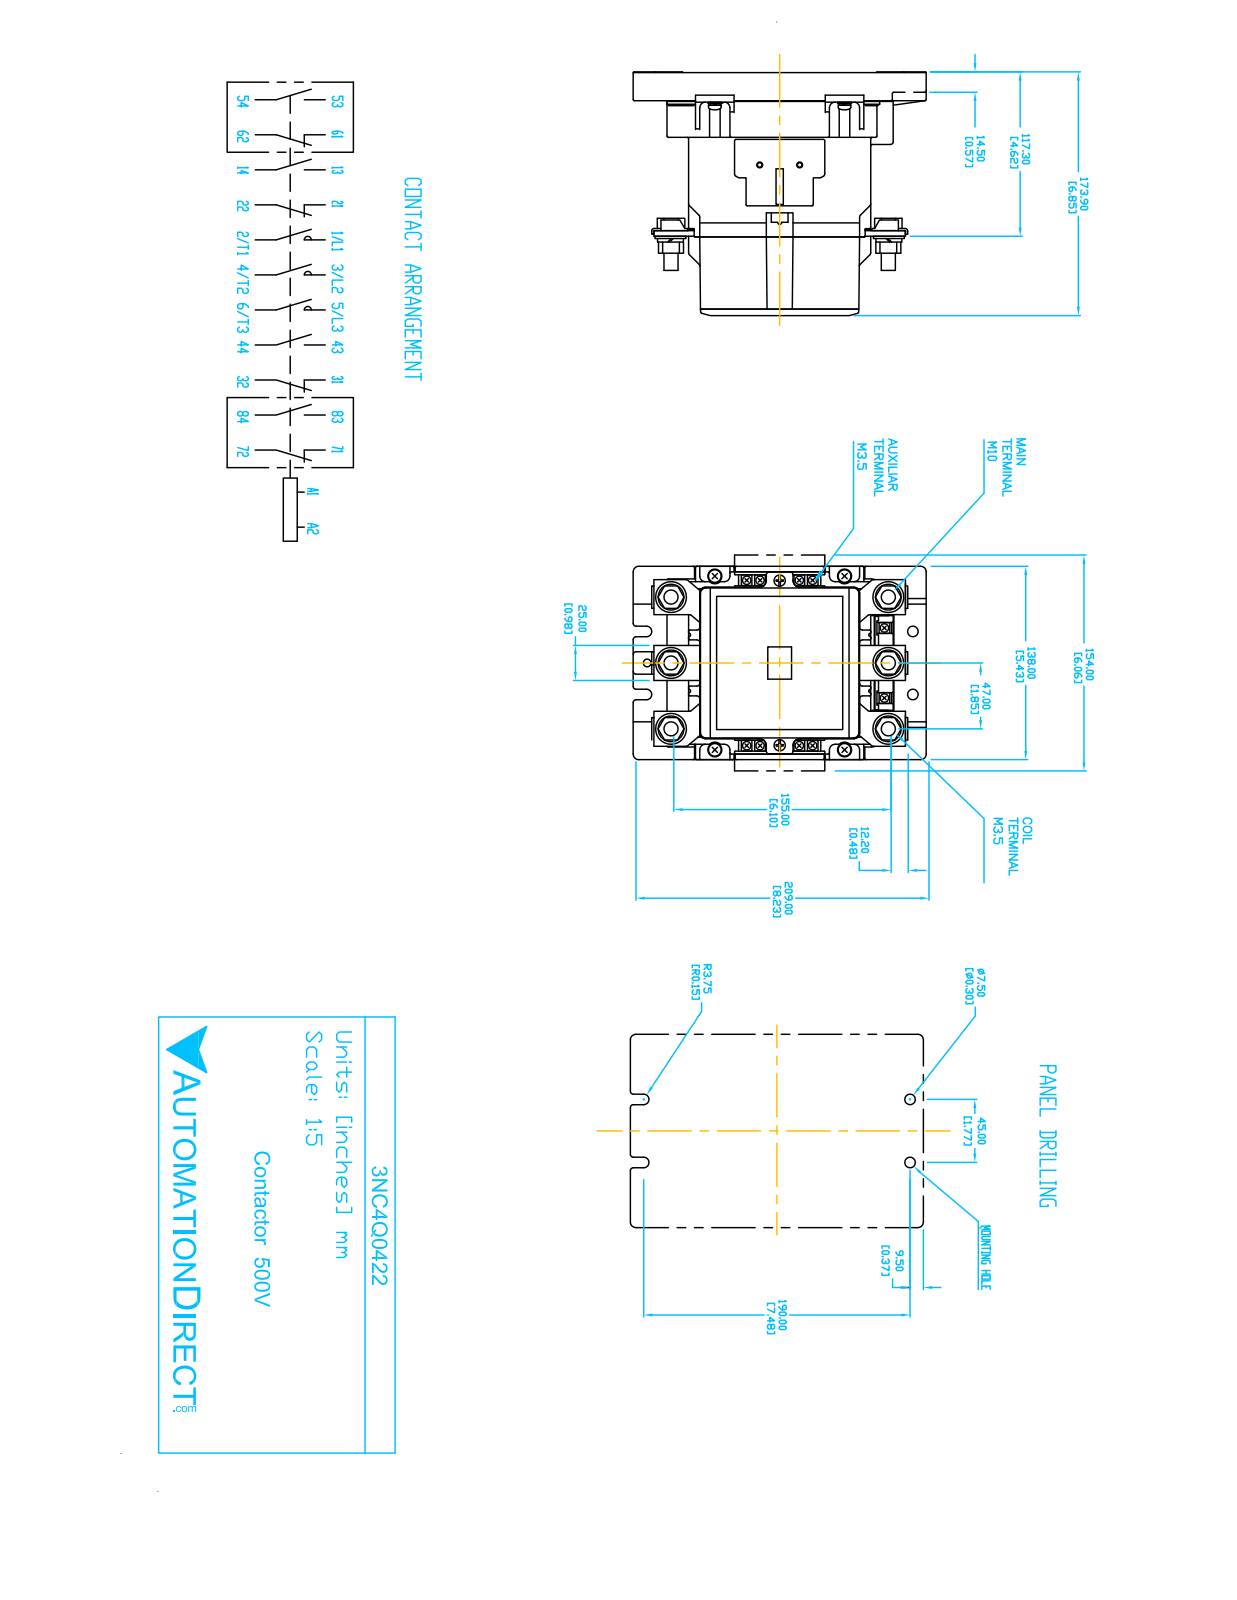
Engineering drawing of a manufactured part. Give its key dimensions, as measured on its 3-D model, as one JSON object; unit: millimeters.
{"part_name": "3NC4Q0422", "step_written_by": "SolidWorks 2018 (AUTOMOTIVE_DESIGN)", "units": "millimeters", "bodies": {"solids": 20, "faces": 376, "planar": 258, "cylindrical": 118, "other": 0}, "overall_size": [209, 176, 138], "volume_mm3": 2943000, "surface_area_mm2": 211000, "round_holes": [[8, 8], [10, 6], [7.5, 2]], "partial_cylinders_radius": [[2, 22], [4, 16], [0.8, 8], [1, 8], [5, 4], [5.5, 4], [0.5, 2], [3.8, 2]], "face_to_face_distances": [119.9, 123, 15, 120.3, 0.4, 108, 176, 56.1, 55.7, 8], "hole_center_spacings": [47, 78.4, 97.4, 131.3, 162, 155, 28.5, 30.1]}
